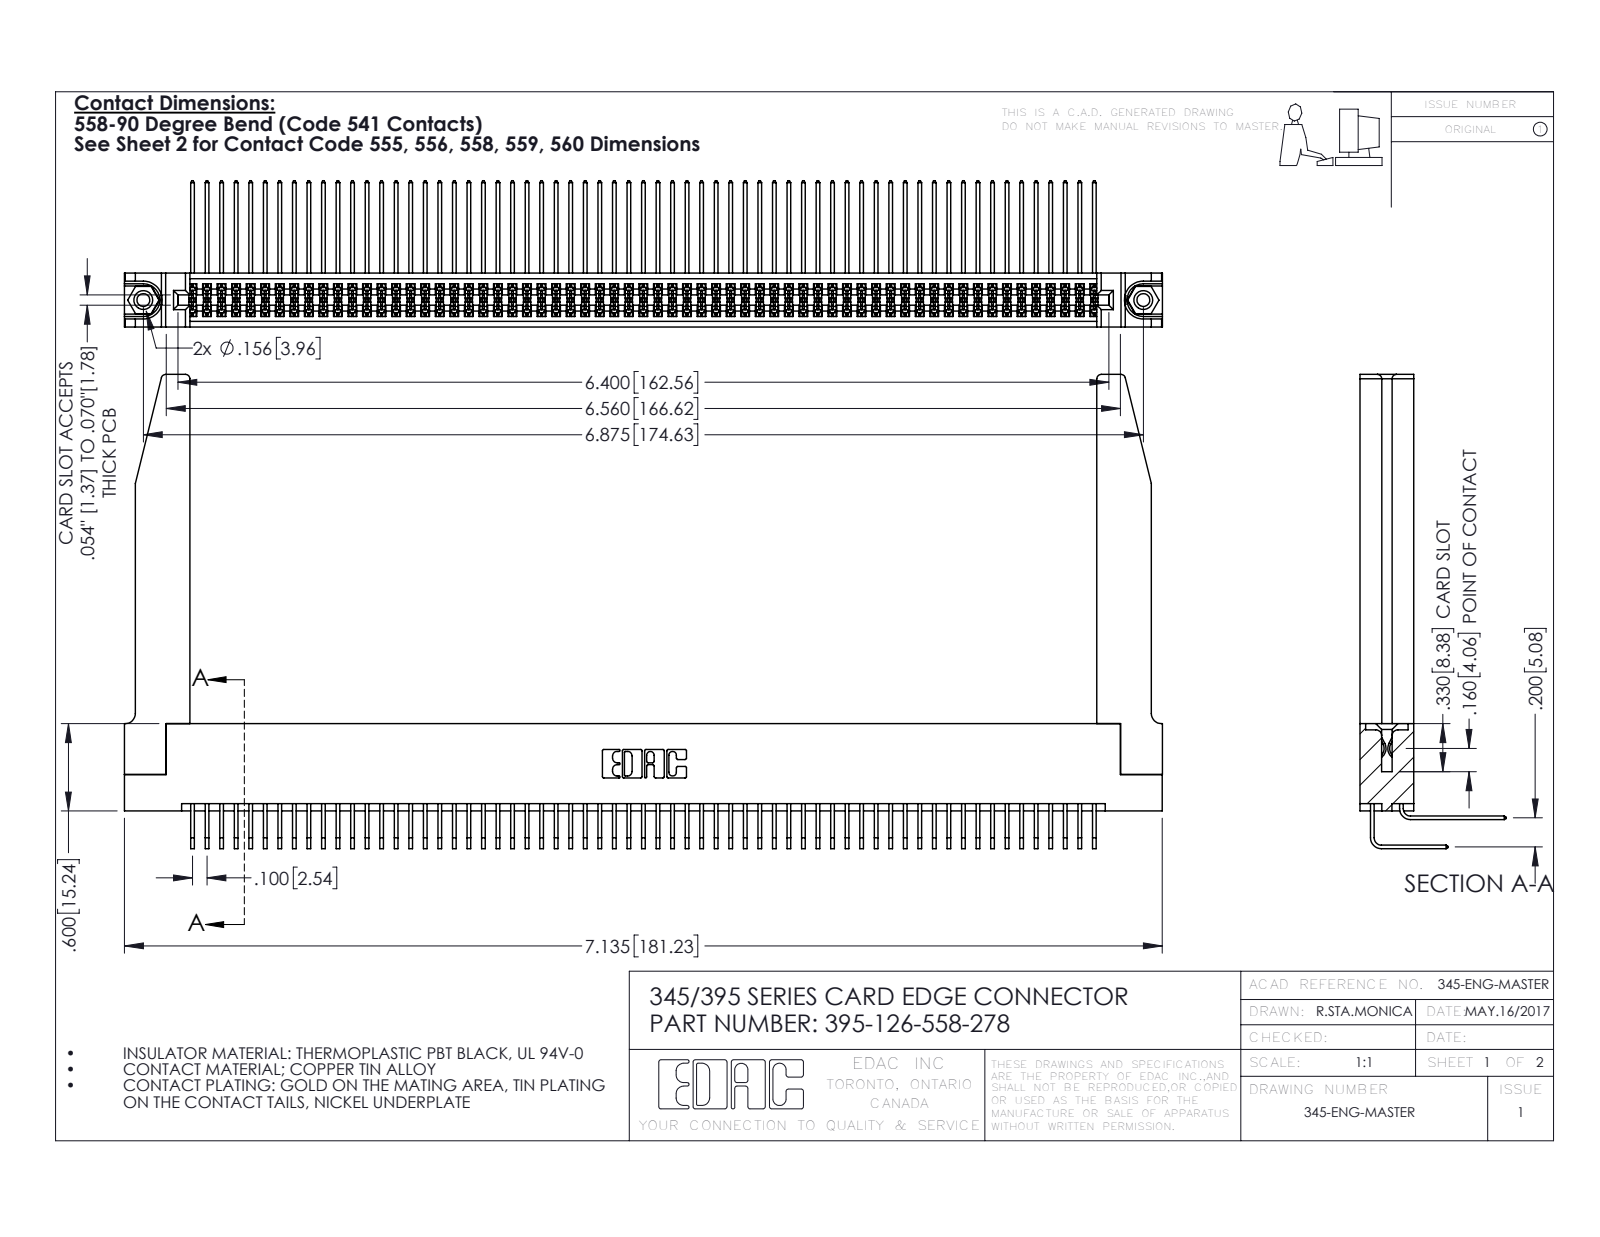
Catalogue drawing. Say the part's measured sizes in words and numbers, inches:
The part is named "395-126-558-278; 345-220-078_345-220-078; 345-292-001_558 Tail - 2; 345-250-001_345-250-001-102 (+2 more)". Its 3-D file was written by "SolidWorks 2016 (CONFIG_CONTROL_DESIGN)". It is 131 solids with 6912 faces: 4632 planar, 2228 cylindrical and 52 other. Overall it measures 7.136 by 3.259 by 1.005 inches. Its volume is 1.605 cubic inches and its surface area 58.98 square inches. Round holes: 2 of diameter 0.089, 2 of diameter 0.125, 2 of diameter 0.156, 1 of diameter 0.064. Round bosses or shafts: 2 of diameter 0.155. Partial cylindrical surfaces (rounded edges, fillets, slot ends): 190 of radius 0.006, 22 of radius 0.01, 8 of radius 0.03, 6 of radius 0.007, 6 of radius 0.031, 3 of radius 0.026, 2 of radius 0.014, 2 of radius 0.019. The main face-to-face distances are 0.072, 0.298, 0.37, 0.2, 0.098, 0.272, 0.025, 0.225, 0.025, 0.285. The hole center spacings are 0.27, 6.639, 6.875.
